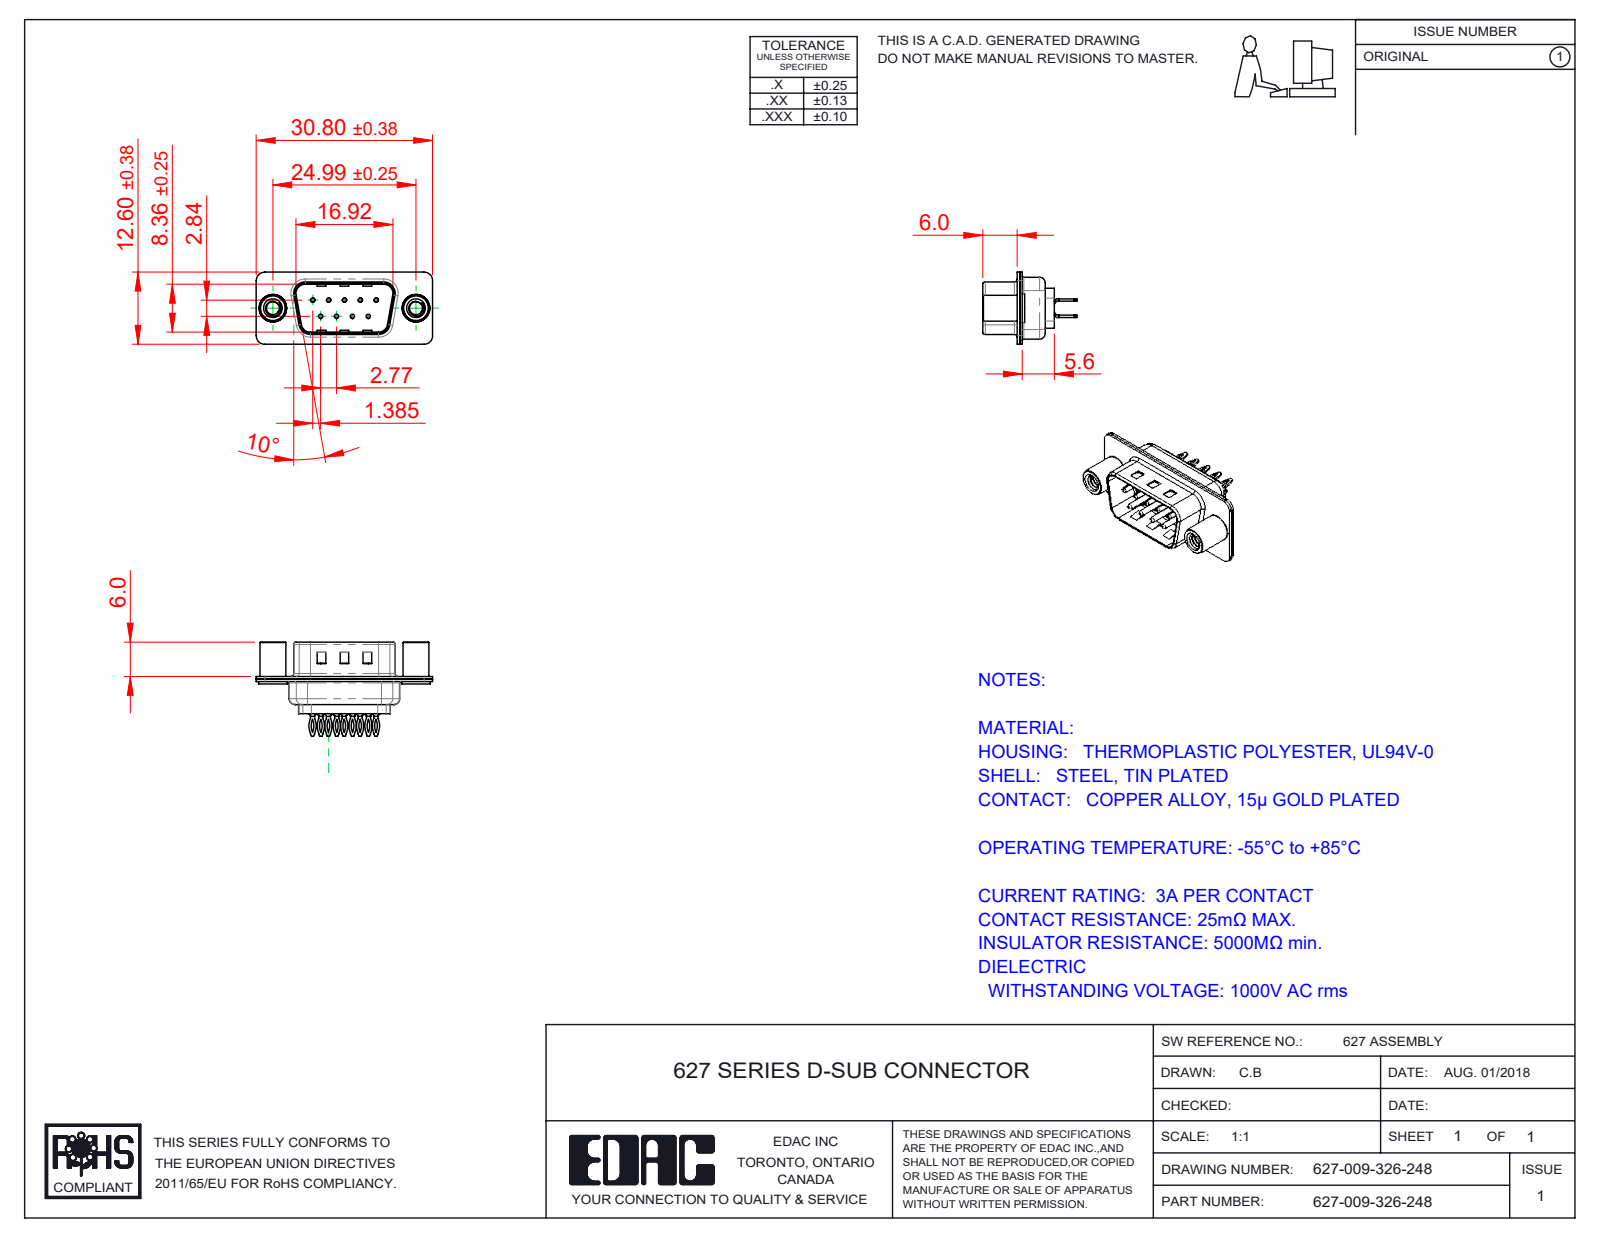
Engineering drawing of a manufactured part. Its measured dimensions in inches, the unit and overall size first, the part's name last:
Units: inches
Overall size (bounding box): 1.213 × 0.648 × 0.496
Round holes (diameter × count): ⌀0.014 ×9, ⌀0.043 ×9, ⌀0.063 ×9, ⌀0.089 ×2, ⌀0.157 ×2, ⌀0.189 ×2
Round bosses / shafts (diameter × count): ⌀0.079 ×9, ⌀0.059 ×9, ⌀0.03 ×9, ⌀0.197 ×2, ⌀0.193 ×2, ⌀0.177 ×2
Partial cylindrical surfaces — rounded edges, fillets, slot ends (radius × count): R0.059 ×18, R0.115 ×18, R0.131 ×18, R0.079 ×12, R0.02 ×8, R0.063 ×8, R0.01 ×4, R0.024 ×4
Main face-to-face distances: 0.016, 0.018, 0.035, 0.032, 0.377, 0.055, 0.345, 0.02, 0.059, 0.238
Hole centre spacings: 0.124, 0.109, 0.218, 0.198, 0.198, 0.327, 0.294, 0.295
Volume: 0.084 in³ · Surface area: 6.355 in²
Bodies: 14 solids, 1022 faces (289 planar, 436 cylindrical, 297 other)
Part name (STEP PRODUCT): 627 Shell Rear_09 Contacts; 627 Contact Row 1_26L; 627 4-40 Threaded Standoff; 627-009-326-248 (+3 more)
STEP written by: SolidWorks 2020 (CONFIG_CONTROL_DESIGN)
